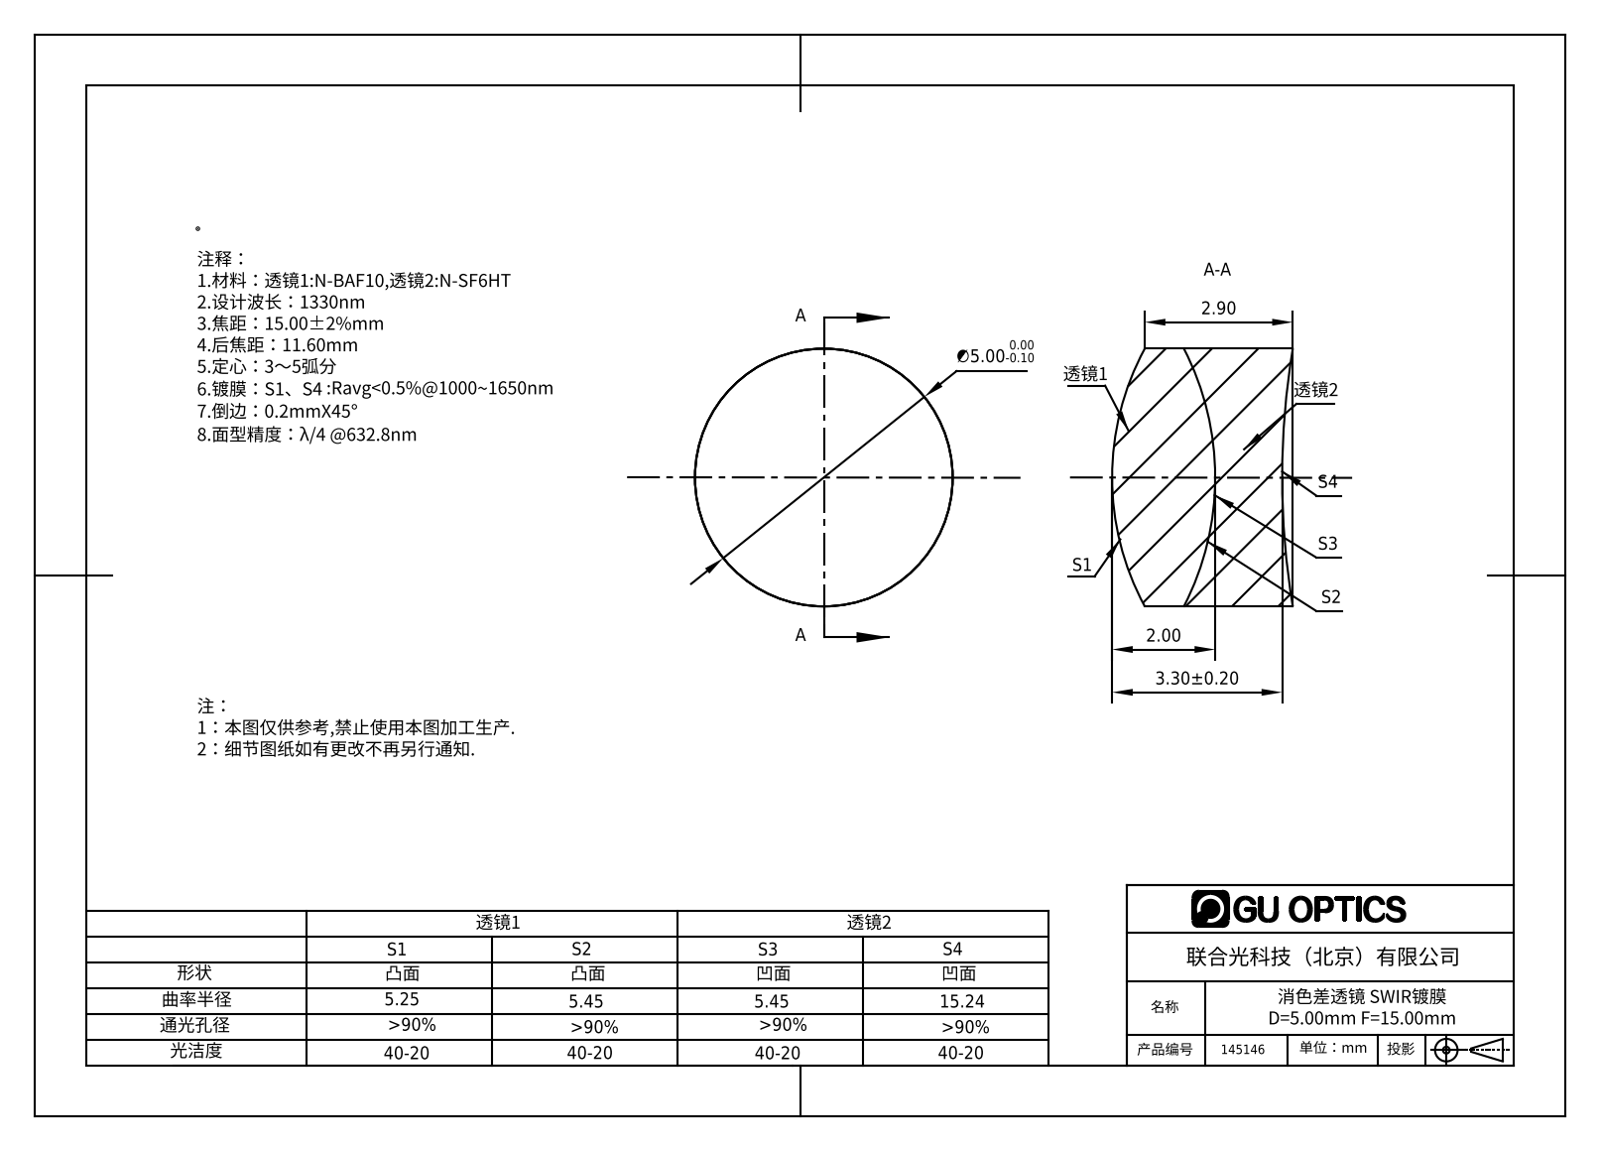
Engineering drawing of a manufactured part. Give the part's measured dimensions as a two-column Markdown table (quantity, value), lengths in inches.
| quantity | value |
| --- | --- |
| part name | 145146 |
| STEP written by | SolidWorks 2016 (AUTOMOTIVE_DESIGN) |
| units | inches |
| bodies | 2 solids, 12 faces (0 planar, 4 cylindrical, 8 other) |
| overall size | 0.197 × 0.197 × 0.138 |
| volume | 0.004 in³ |
| surface area | 0.197 in² |
| round bosses / shafts (diameter × count) | 0.197 × 1 |
